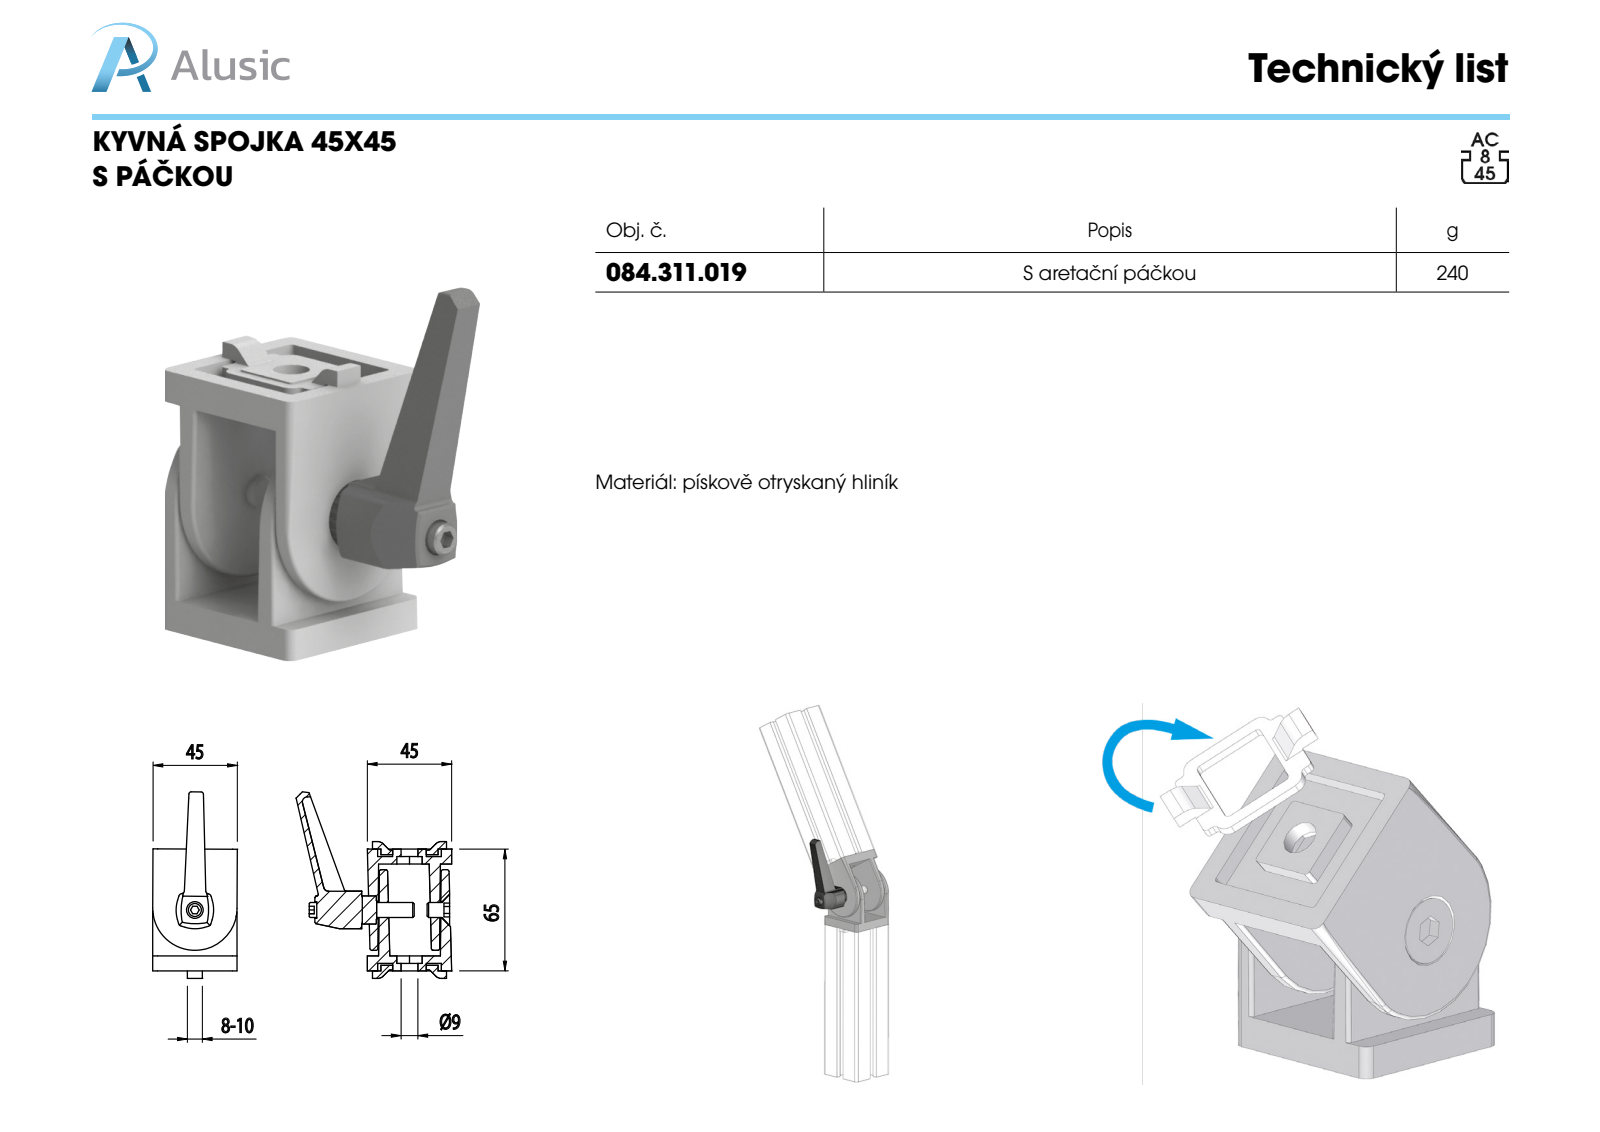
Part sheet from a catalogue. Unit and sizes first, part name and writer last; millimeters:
Units: millimetres
Overall size (bounding box): 95.53 × 83 × 45.16
Round holes (diameter × count): ⌀9 ×3, ⌀6.8 ×1, ⌀8.89 ×1
Round bosses / shafts (diameter × count): ⌀16 ×1, ⌀15 ×1, ⌀13 ×1, ⌀10 ×1, ⌀8 ×1
Partial cylindrical surfaces — rounded edges, fillets, slot ends (radius × count): R1 ×38, R2.5 ×8, R1.93 ×4, R3 ×4, R1.2 ×3, R18.22 ×3, R1.5 ×2, R2.67 ×2
Main face-to-face distances: 4, 8, 10.5, 43.31, 32.8, 22.3, 32.81, 10.51, 32.59, 33.02
Volume: 76 581 mm³ · Surface area: 36 951 mm²
Bodies: 5 solids, 381 faces (167 planar, 145 cylindrical, 69 other)
Part name (STEP PRODUCT): 084.311.019; MR.63 p-M8x16; 084.311.010-2; VITI TSEI UNI 5933_M8x12 UNI 5933 (+1 more)
STEP written by: SolidWorks 2012 (CONFIG_CONTROL_DESIGN)
